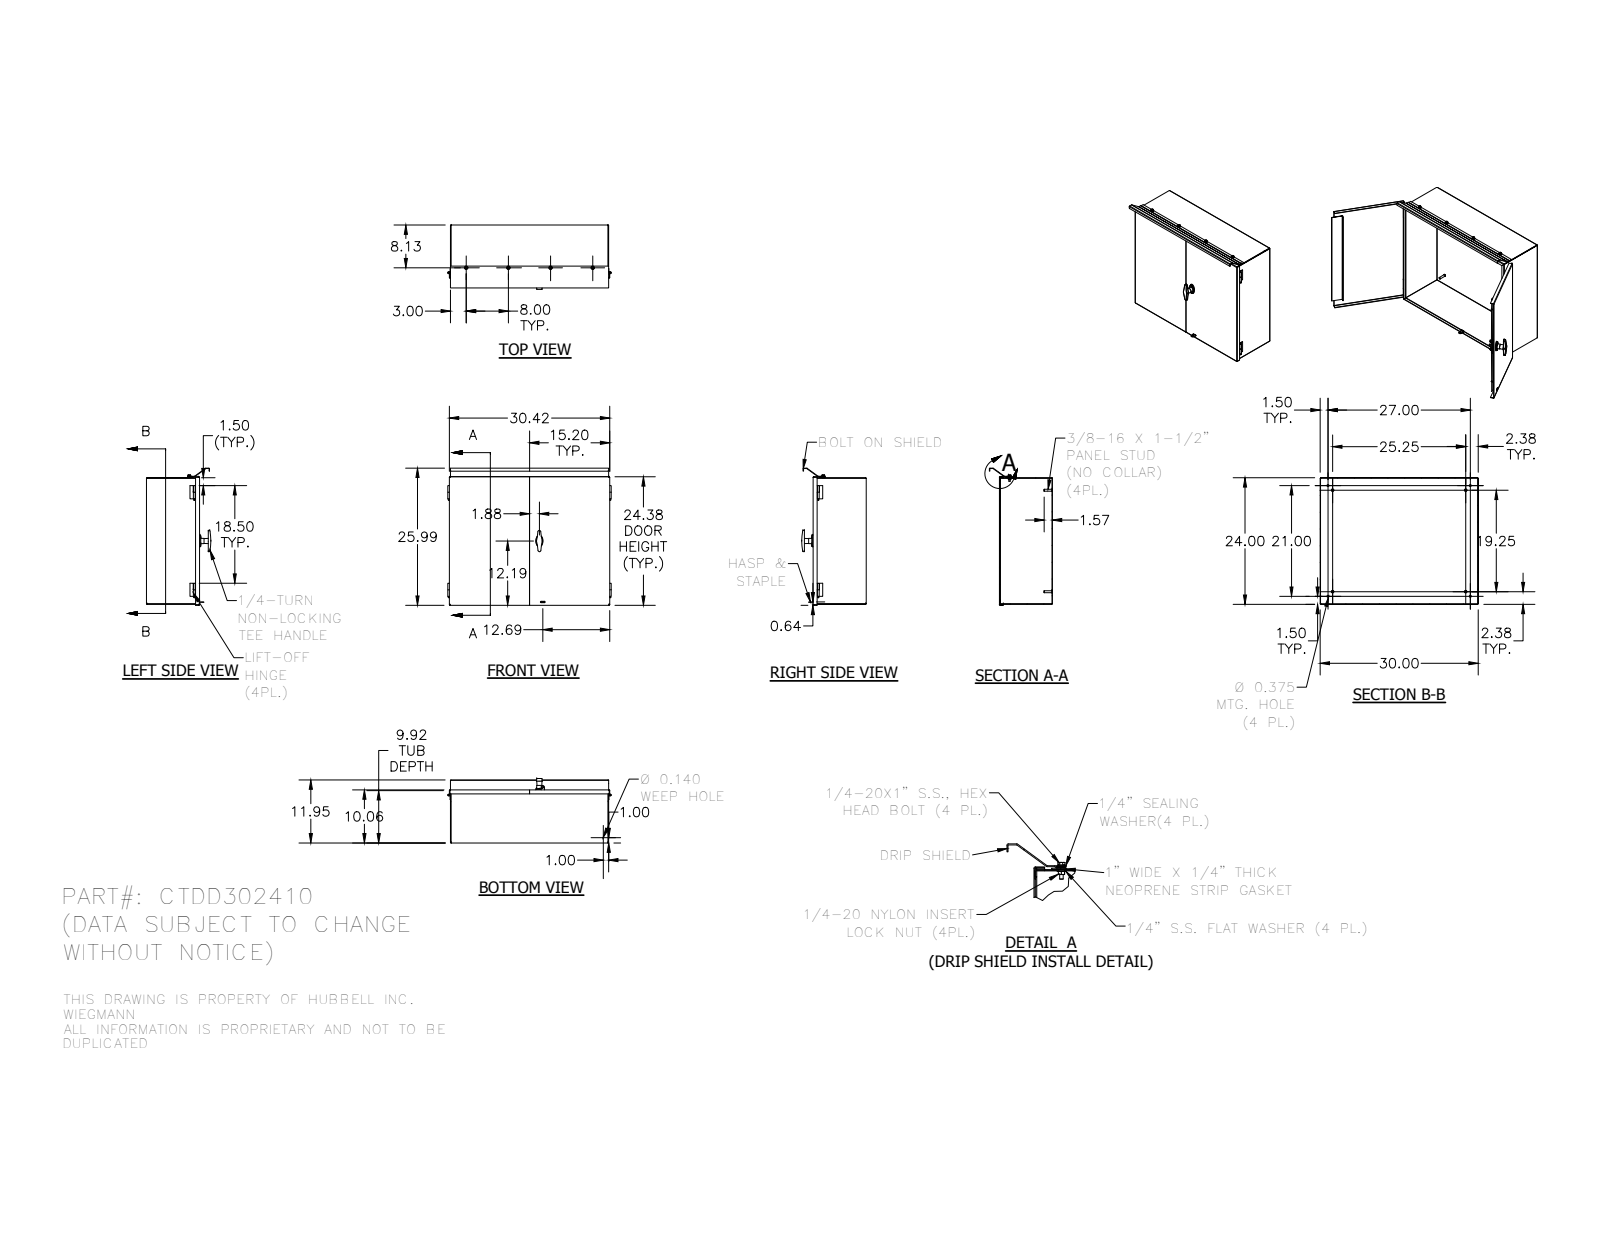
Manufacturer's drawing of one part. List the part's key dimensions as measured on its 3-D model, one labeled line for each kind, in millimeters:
Part name (STEP PRODUCT): CTDD302410BKP; 38822; HC2527; HFW328178 (+8 more)
STEP written by: Autodesk Inventor 2014 (AUTOMOTIVE_DESIGN)
Units: millimetres
Bodies: 55 solids, 1004 faces (546 planar, 232 cylindrical, 226 other)
Overall size (bounding box): 787.4 × 660.27 × 310.25
Volume: 3 845 000 mm³ · Surface area: 3 997 000 mm²
Round holes (diameter × count): ⌀4.98 ×6, ⌀7.14 ×6, ⌀9.52 ×5, ⌀5.97 ×4, ⌀6.99 ×4, ⌀7.37 ×4, ⌀4.06 ×2, ⌀5.36 ×2, ⌀5.56 ×2, ⌀6.35 ×2, ⌀7.14 ×2, ⌀2.38 ×1
Round bosses / shafts (diameter × count): ⌀11.13 ×6, ⌀6.35 ×6, ⌀16.51 ×4, ⌀15.88 ×4, ⌀15.24 ×4, ⌀11.73 ×4, ⌀9.52 ×4, ⌀6.6 ×4
Partial cylindrical surfaces — rounded edges, fillets, slot ends (radius × count): R0.79 ×25, R2.67 ×19, R1.78 ×16, R1.59 ×6, R3.17 ×6, R0.2 ×2, R1.59 ×2, R3.17 ×2
Main face-to-face distances: 1.88, 253.6, 251.72, 255.48, 607.72, 1.87, 609.6, 605.84, 762, 760.12
Hole centre spacings: 203.2, 19.05, 385.54, 398.04, 406.4, 411.05, 462.26, 472.74
